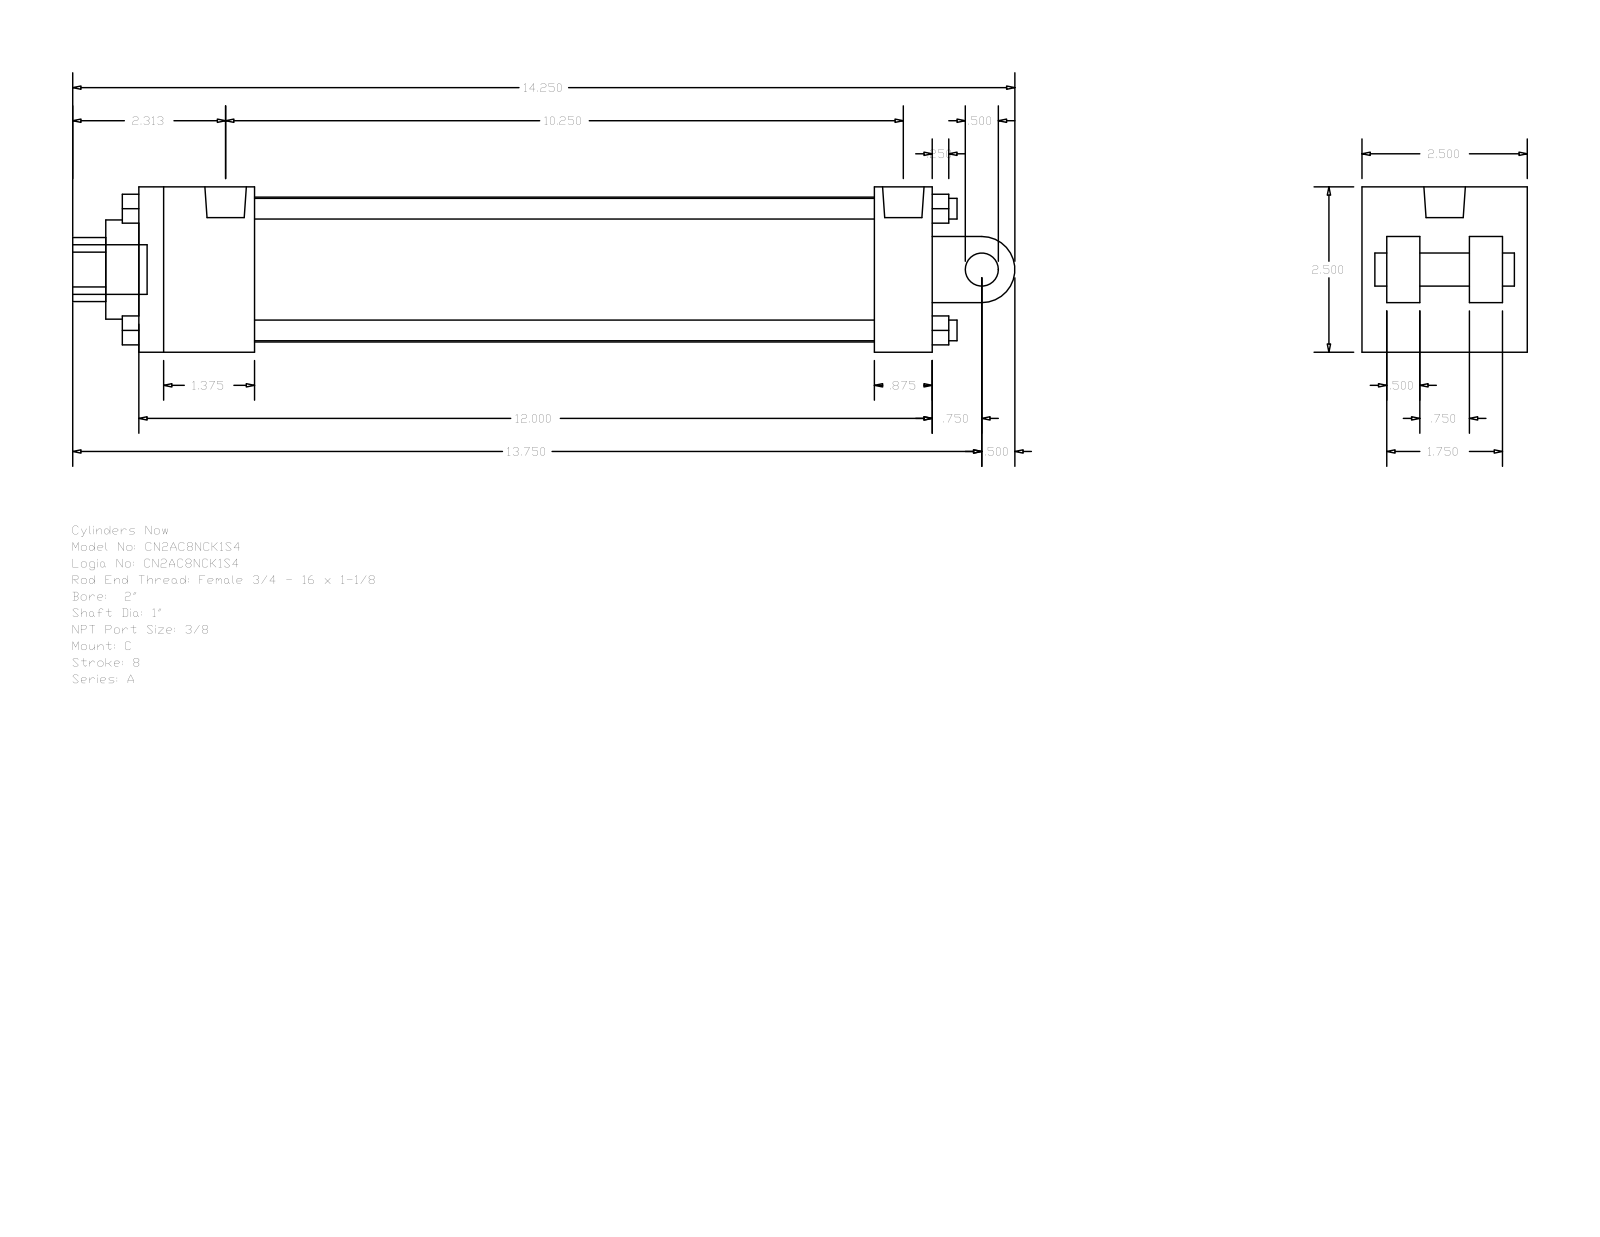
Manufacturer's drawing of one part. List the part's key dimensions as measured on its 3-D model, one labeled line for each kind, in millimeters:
Part name (STEP PRODUCT): A_C__0200_1
STEP written by: GSSL Pune (CONFIG_CONTROL_DESIGN)
Units: millimetres
Bodies: 0 solids, 135 faces (102 planar, 33 cylindrical, 0 other)
Overall size (bounding box): 361.95 × 63.5 × 63.5
Round holes (diameter × count): ⌀5.56 ×2, ⌀15.93 ×1, ⌀25.4 ×1, ⌀38.1 ×1, ⌀55.63 ×1
Round bosses / shafts (diameter × count): ⌀7.94 ×4, ⌀5.56 ×2, ⌀19.05 ×1, ⌀15.93 ×1, ⌀12.7 ×1
Partial cylindrical surfaces — rounded edges, fillets, slot ends (radius × count): R12.29 ×1, R12.7 ×1
Main face-to-face distances: 63.5, 22.22, 304.8, 44.45, 12.7, 9.52, 41.28, 260.35, 282.58, 238.13
Hole centre spacings: 3.98
